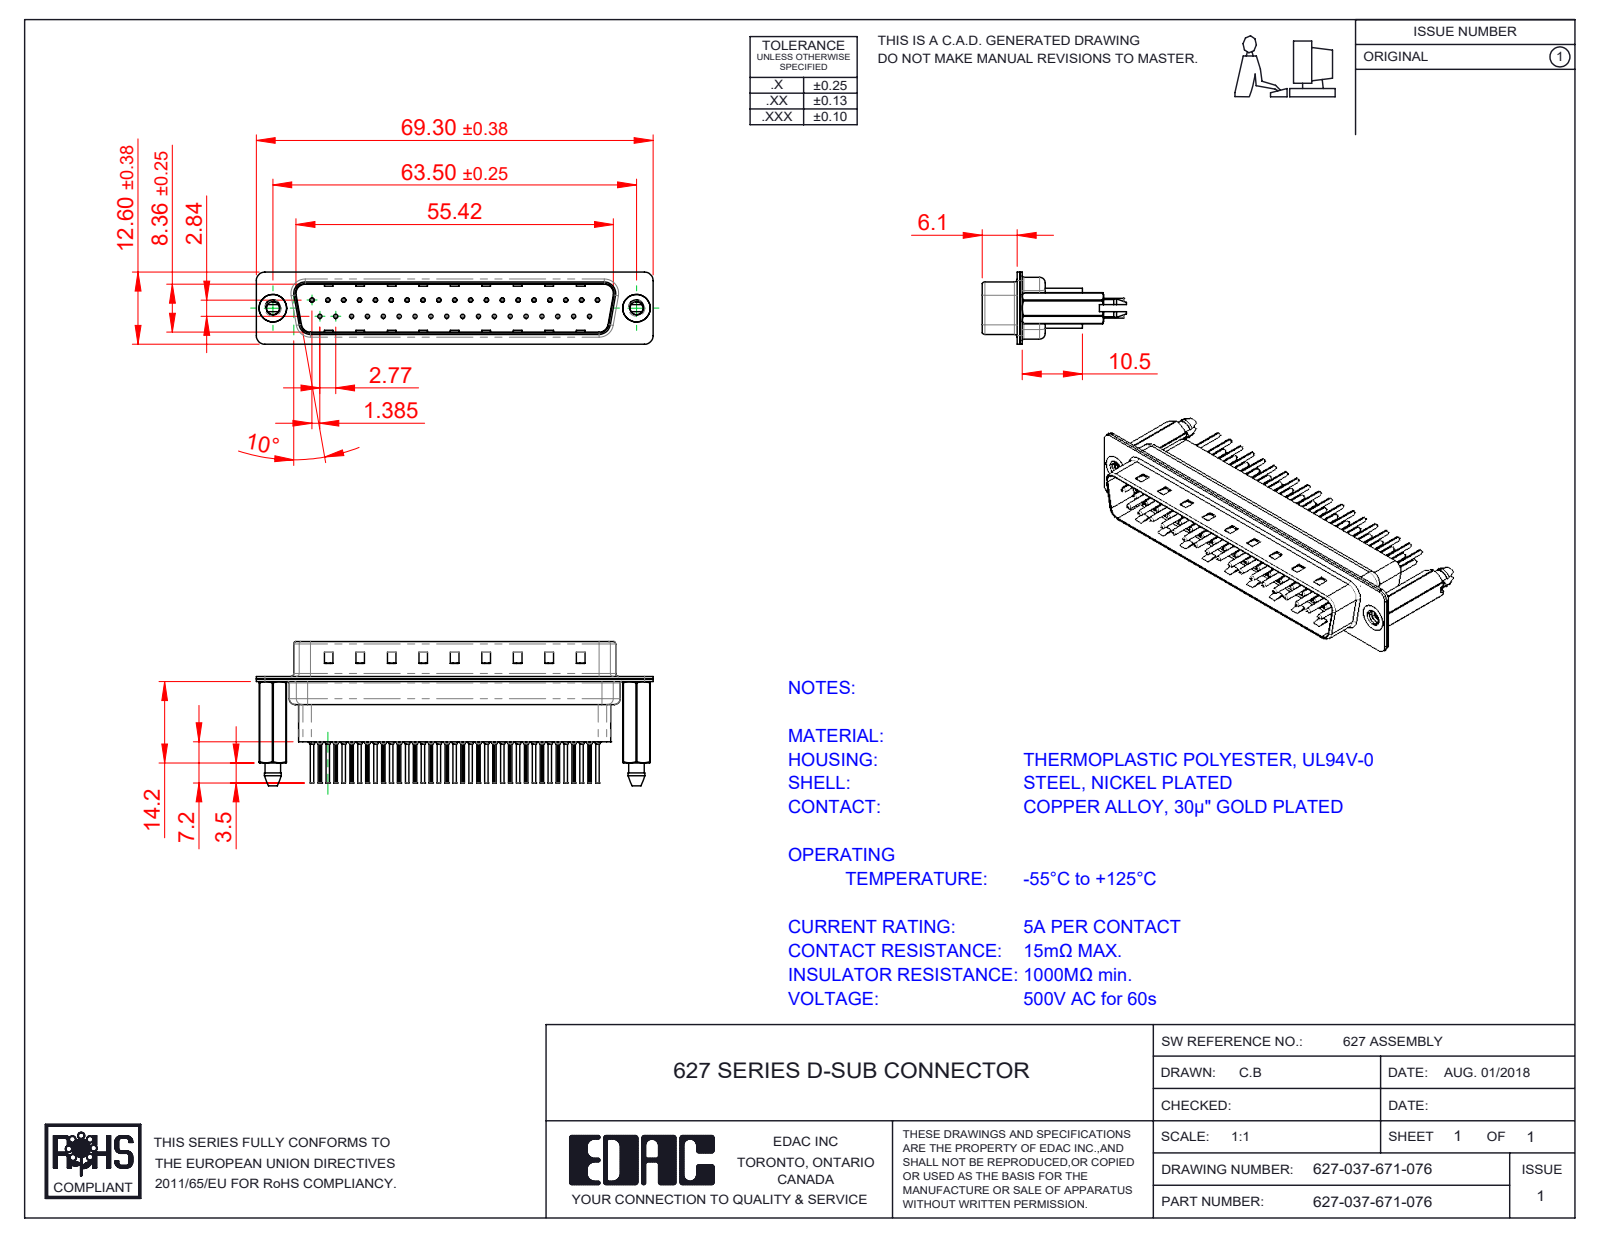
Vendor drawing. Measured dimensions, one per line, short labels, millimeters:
name: 627 Housing_37 HP; 627 Contact Row 1_61; 627 Contact Row 2_61; 627 Shell Front_37 Contacts (+3 more)
written by: SolidWorks 2020 (CONFIG_CONTROL_DESIGN)
unit: mm
bodies: 42 solids, 4146 faces (1123 planar, 1576 cylindrical, 1447 other)
size: 69.3 × 25.1 × 12.6
volume: 5 699 mm³; area: 14 707 mm²
holes: 37× ⌀0.2, 37× ⌀0.35, 37× ⌀1.1, 37× ⌀1.6, 2× ⌀2.26, 2× ⌀4, 2× ⌀4.8
bosses: 37× ⌀2, 37× ⌀1.5, 37× ⌀0.75, 37× ⌀0.6, 2× ⌀4.9
rounds: 74× R0.1, 18× R1.5, 12× R2, 10× R1.6, 8× R0.5, 4× R0.25, 4× R0.6, 4× R0.65
face distances: 0.4, 0.82, 9.58, 0.68, 7.68, 0.45, 1.5, 1.08, 8.08, 8.76
hole spacings: 3.16, 2.77, 5.54, 8.31, 5.04, 10.1, 11.08, 12.78
